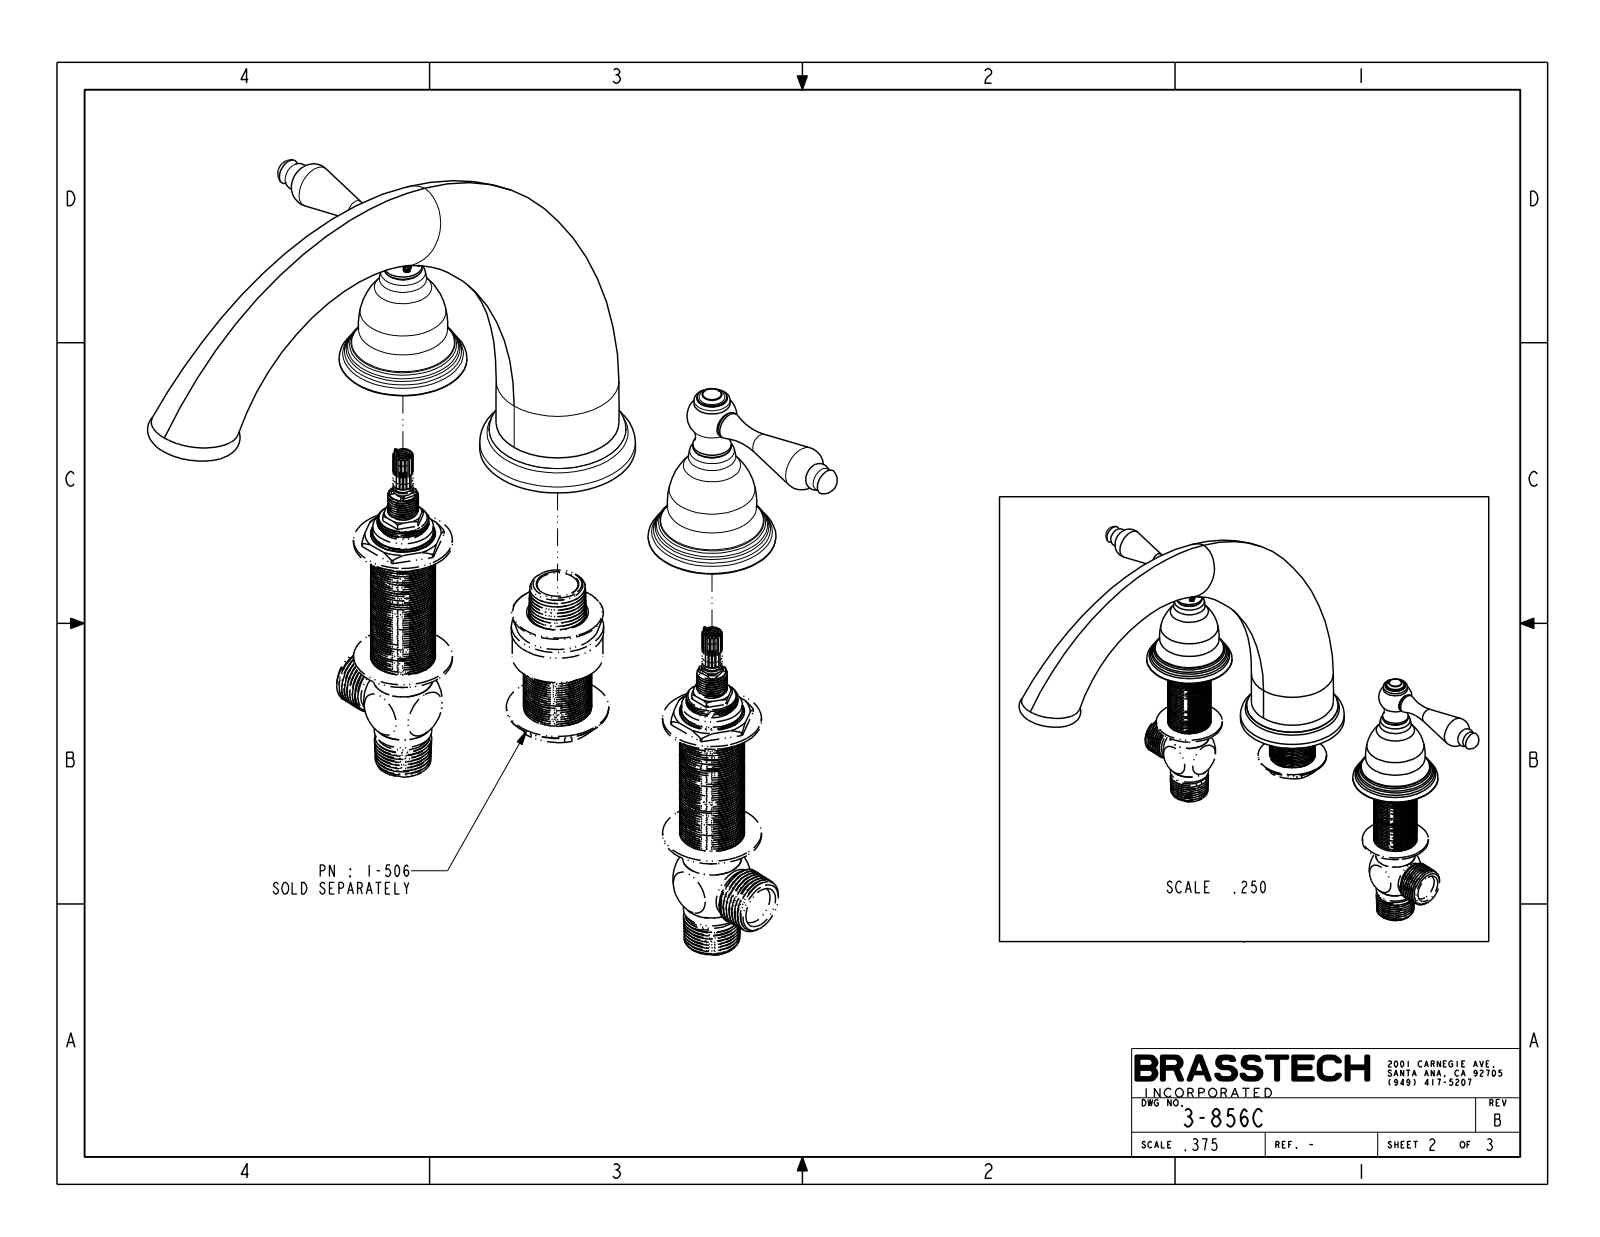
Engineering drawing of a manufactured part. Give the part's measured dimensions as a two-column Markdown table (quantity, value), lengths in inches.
| quantity | value |
| --- | --- |
| part name | 3-856C |
| STEP written by | CREO PARAMETRIC BY PTC INC, 2018400 (CONFIG_CONTROL_DESIGN) |
| units | inches |
| bodies | 3 solids, 162 faces (20 planar, 28 cylindrical, 114 other) |
| overall size | 14.274 × 11.68 × 7.801 |
| volume | 46.27 in³ |
| surface area | 137 in² |
| round bosses / shafts (diameter × count) | 2.34 × 2, 0.705 × 2, 0.661 × 2, 0.544 × 2, 0.4 × 2, 2.85 × 1, 2.506 × 1, 0.5 × 1 |
| main face-to-face distances | 2.039, 2.008, 0.031, 3.209, 1.201, 1.17, 0.575, 1.433, 1.465, 2.634 |
